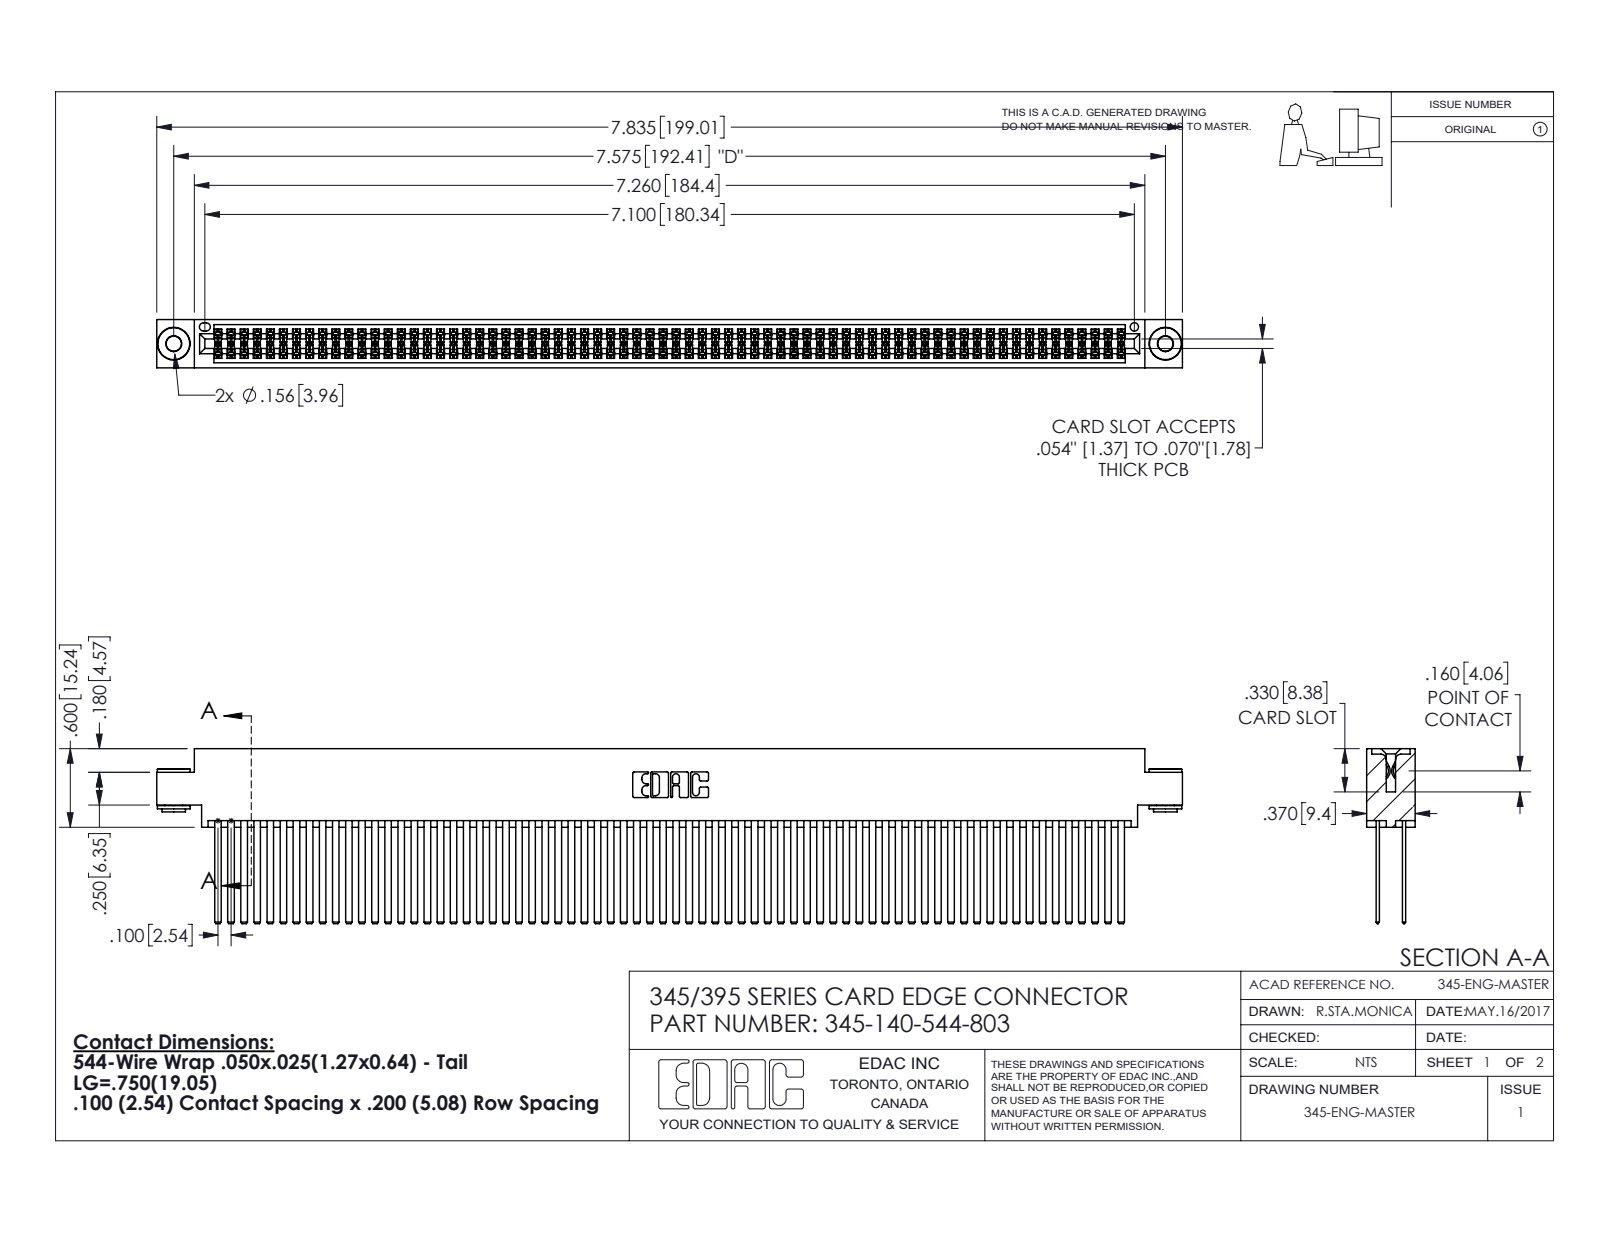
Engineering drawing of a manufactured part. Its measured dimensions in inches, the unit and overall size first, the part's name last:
Units: inches
Overall size (bounding box): 7.835 × 1.337 × 0.37
Round holes (diameter × count): ⌀0.116 ×2, ⌀0.156 ×2, ⌀0.064 ×1
Round bosses / shafts (diameter × count): ⌀0.25 ×2, ⌀0.18 ×2, ⌀0.136 ×2
Partial cylindrical surfaces — rounded edges, fillets, slot ends (radius × count): R0.006 ×210, R0.01 ×22, R0.007 ×6, R0.031 ×6, R0.026 ×3, R0.014 ×2, R0.019 ×2, R0.022 ×2
Main face-to-face distances: 0.2, 0.025, 0.072, 0.098, 0.272, 0.298, 0.225, 0.175, 0.37, 0.15
Hole centre spacings: 0.27, 7.339, 7.575
Volume: 1.31 in³ · Surface area: 59.47 in²
Bodies: 143 solids, 6328 faces (4154 planar, 2166 cylindrical, 8 other)
Part name (STEP PRODUCT): 345-292-001_345-293-144; 345-140-544-803; 345-250-002_345-250-002-102; 345 Part_0.170 Offset - 0.156 Dia-TH
STEP written by: SolidWorks 2016 (CONFIG_CONTROL_DESIGN)
